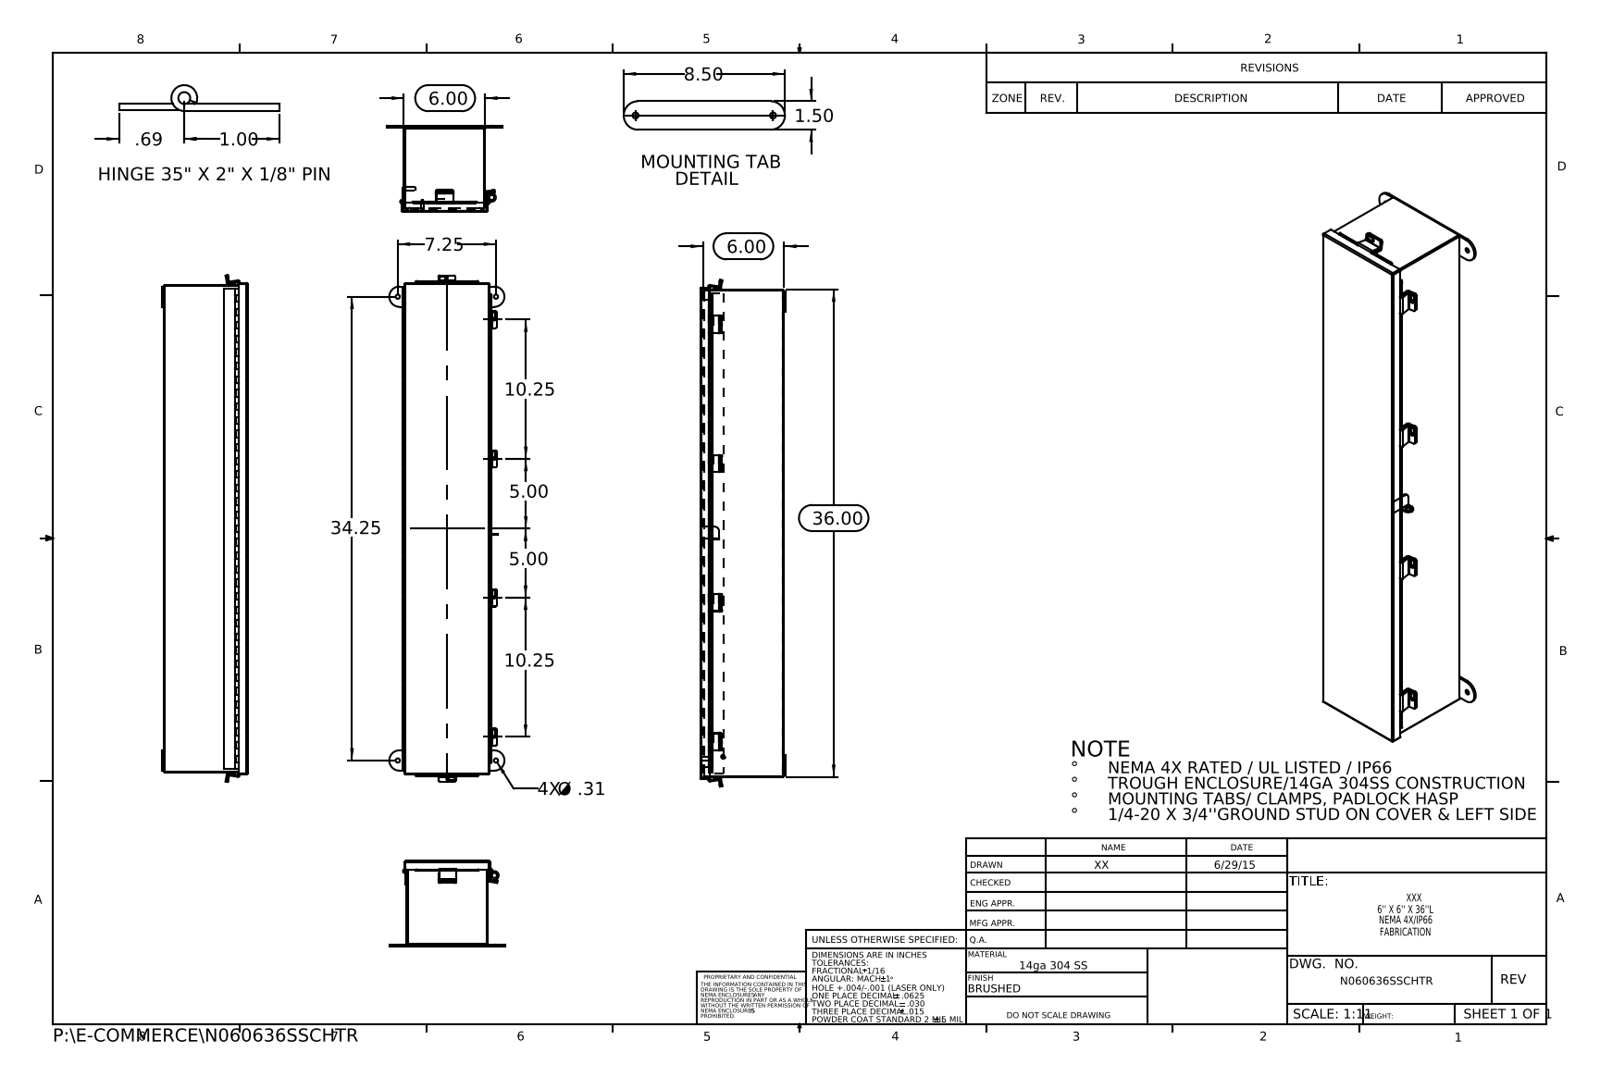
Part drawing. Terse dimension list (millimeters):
name: N060636SSCHTR _JIC Hinge; N060636SSCHTR Hinge Cover Side JIC; N060636SSCHTR Hinge Body Side; N060636SSCHTR (+8 more)
written by: SolidWorks 2015 (CONFIG_CONTROL_DESIGN)
unit: mm
bodies: 23 solids, 1148 faces (697 planar, 431 cylindrical, 20 other)
size: 950.1 × 215.9 × 161
volume: 1 408 000 mm³; area: 1 492 000 mm²
holes: 6× ⌀6.4, 4× ⌀8, 1× ⌀3.2, 1× ⌀3.2, 1× ⌀9.5
bosses: 2× ⌀8, 2× ⌀6, 1× ⌀6.9, 1× ⌀6.4
rounds: 22× R3.2, 12× R0.2, 12× R3.4, 11× R0.3, 11× R2.2, 6× R2.1, 6× R2.5, 4× R19.1
face distances: 1.9, 150.5, 155.7, 152.4, 148.6, 157.6, 153.7, 3.8, 154.3, 1.9
hole spacings: 184.2, 261.3, 522.3, 870, 889.2, 168.2, 261, 783.6
